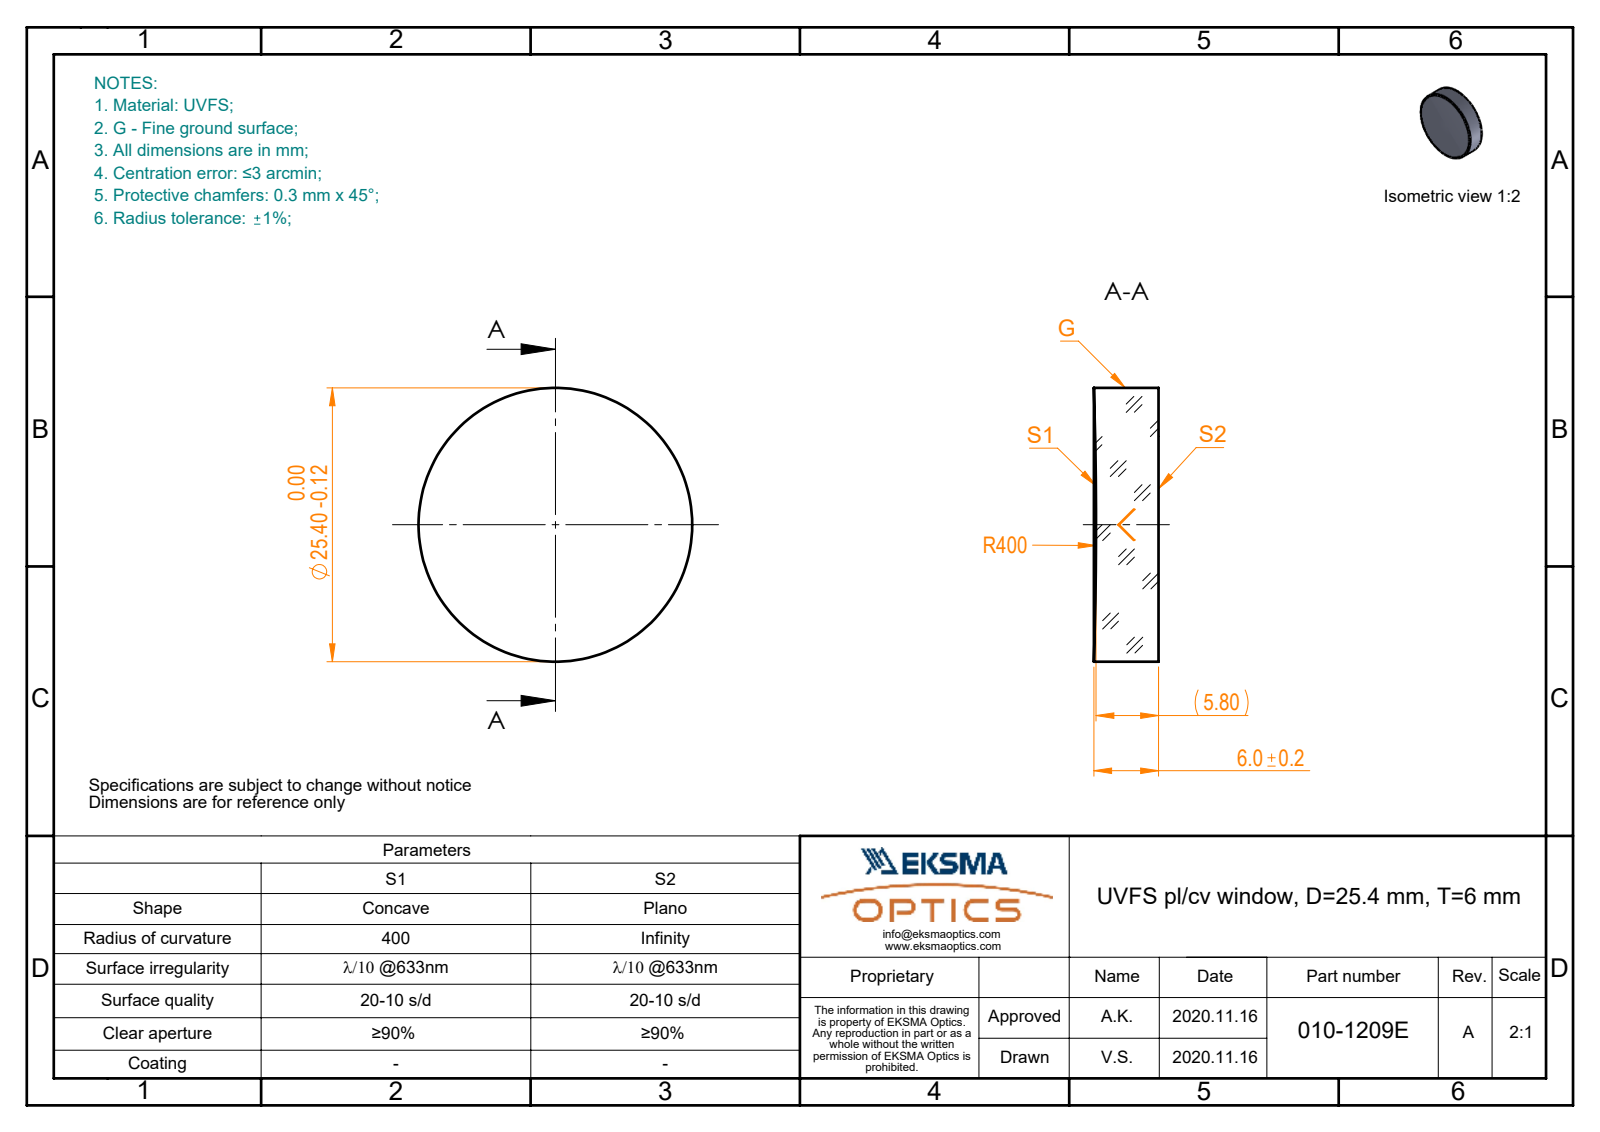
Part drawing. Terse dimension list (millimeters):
name: 010-1209E_UVFS_PCV_window
written by: SolidWorks 2019 (CONFIG_CONTROL_DESIGN)
unit: mm
bodies: 1 solid, 5 faces (1 planar, 2 cylindrical, 2 other)
size: 25.4 × 25.4 × 6
volume: 2 989 mm³; area: 1 492 mm²
bosses: 1× ⌀25.4
